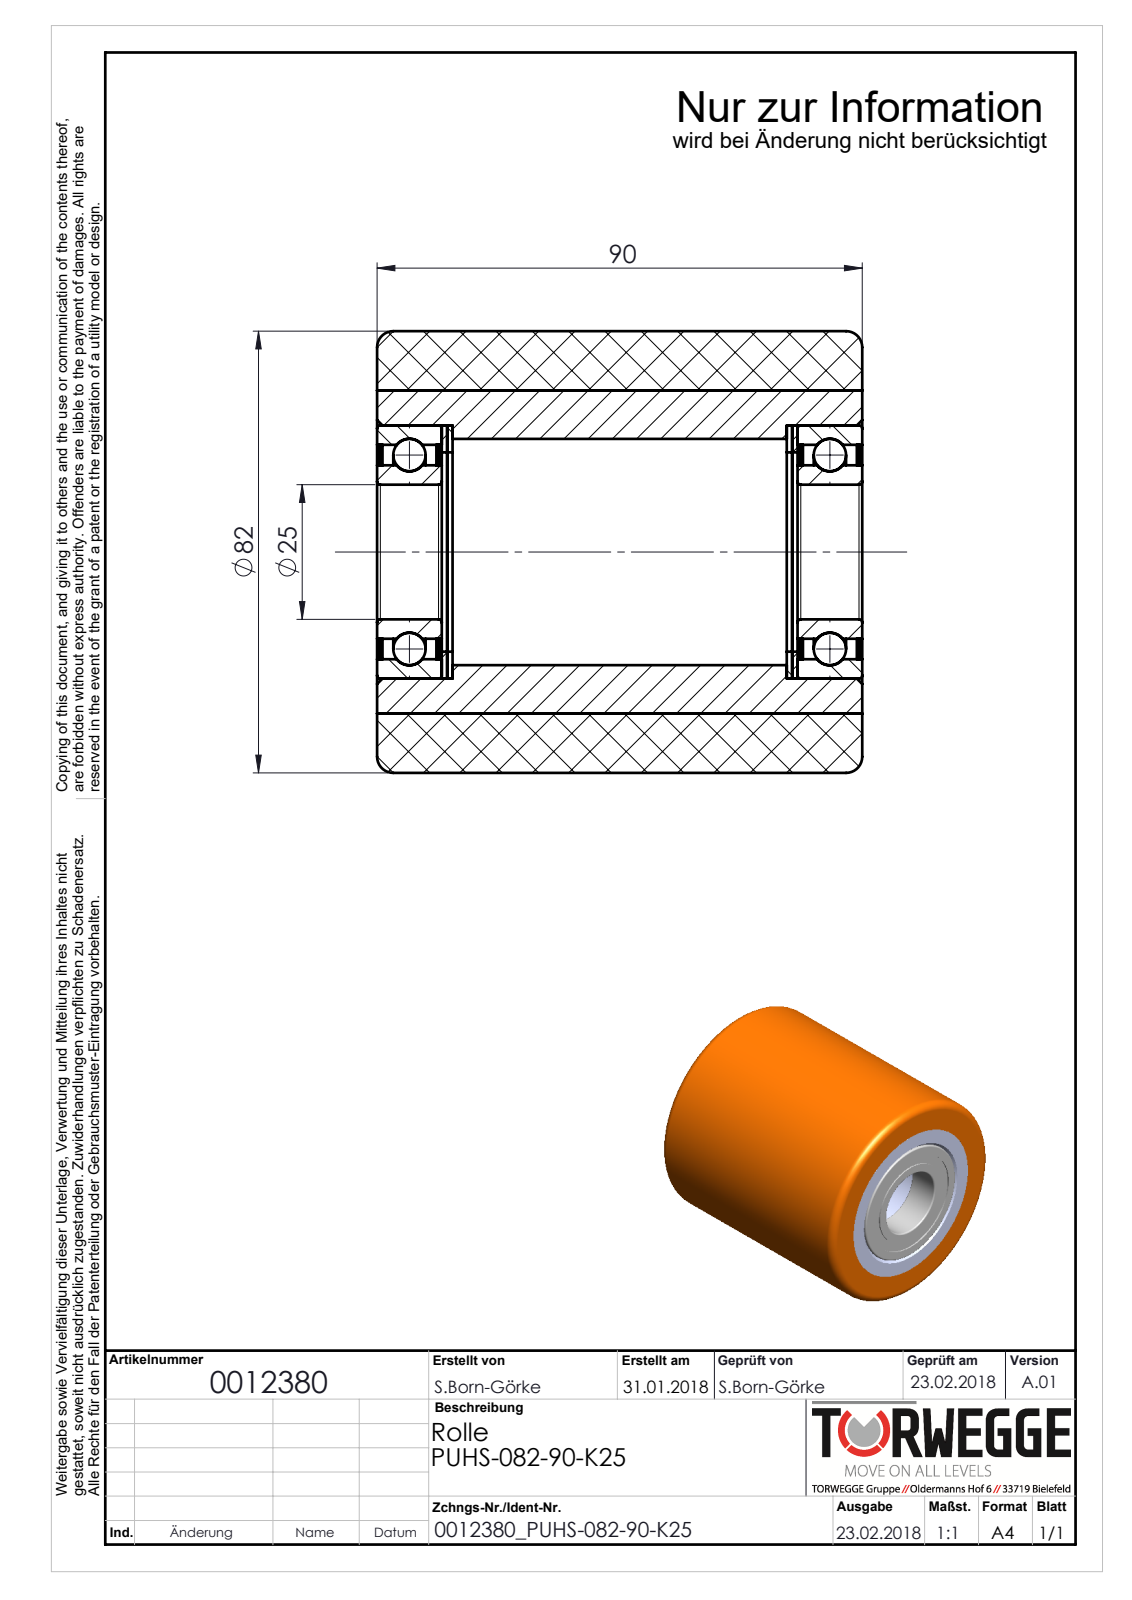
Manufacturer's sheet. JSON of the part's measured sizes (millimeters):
{"part_name": "0012380_PUHS-082-90-K25", "step_written_by": "SolidWorks 2016 (AUTOMOTIVE_DESIGN)", "units": "millimeters", "bodies": {"solids": 16, "faces": 158, "planar": 30, "cylindrical": 68, "other": 60}, "overall_size": [90, 82, 82], "volume_mm3": 367175, "surface_area_mm2": 104948, "round_holes": [[25, 1], [32.2, 1], [37, 1], [39.8, 1], [42, 1], [60, 1]], "round_bosses_or_shafts": [[82, 1], [47, 1]], "face_to_face_distances": [1, 78, 12, 0.5, 13, 77, 65, 90, 64, 76]}
